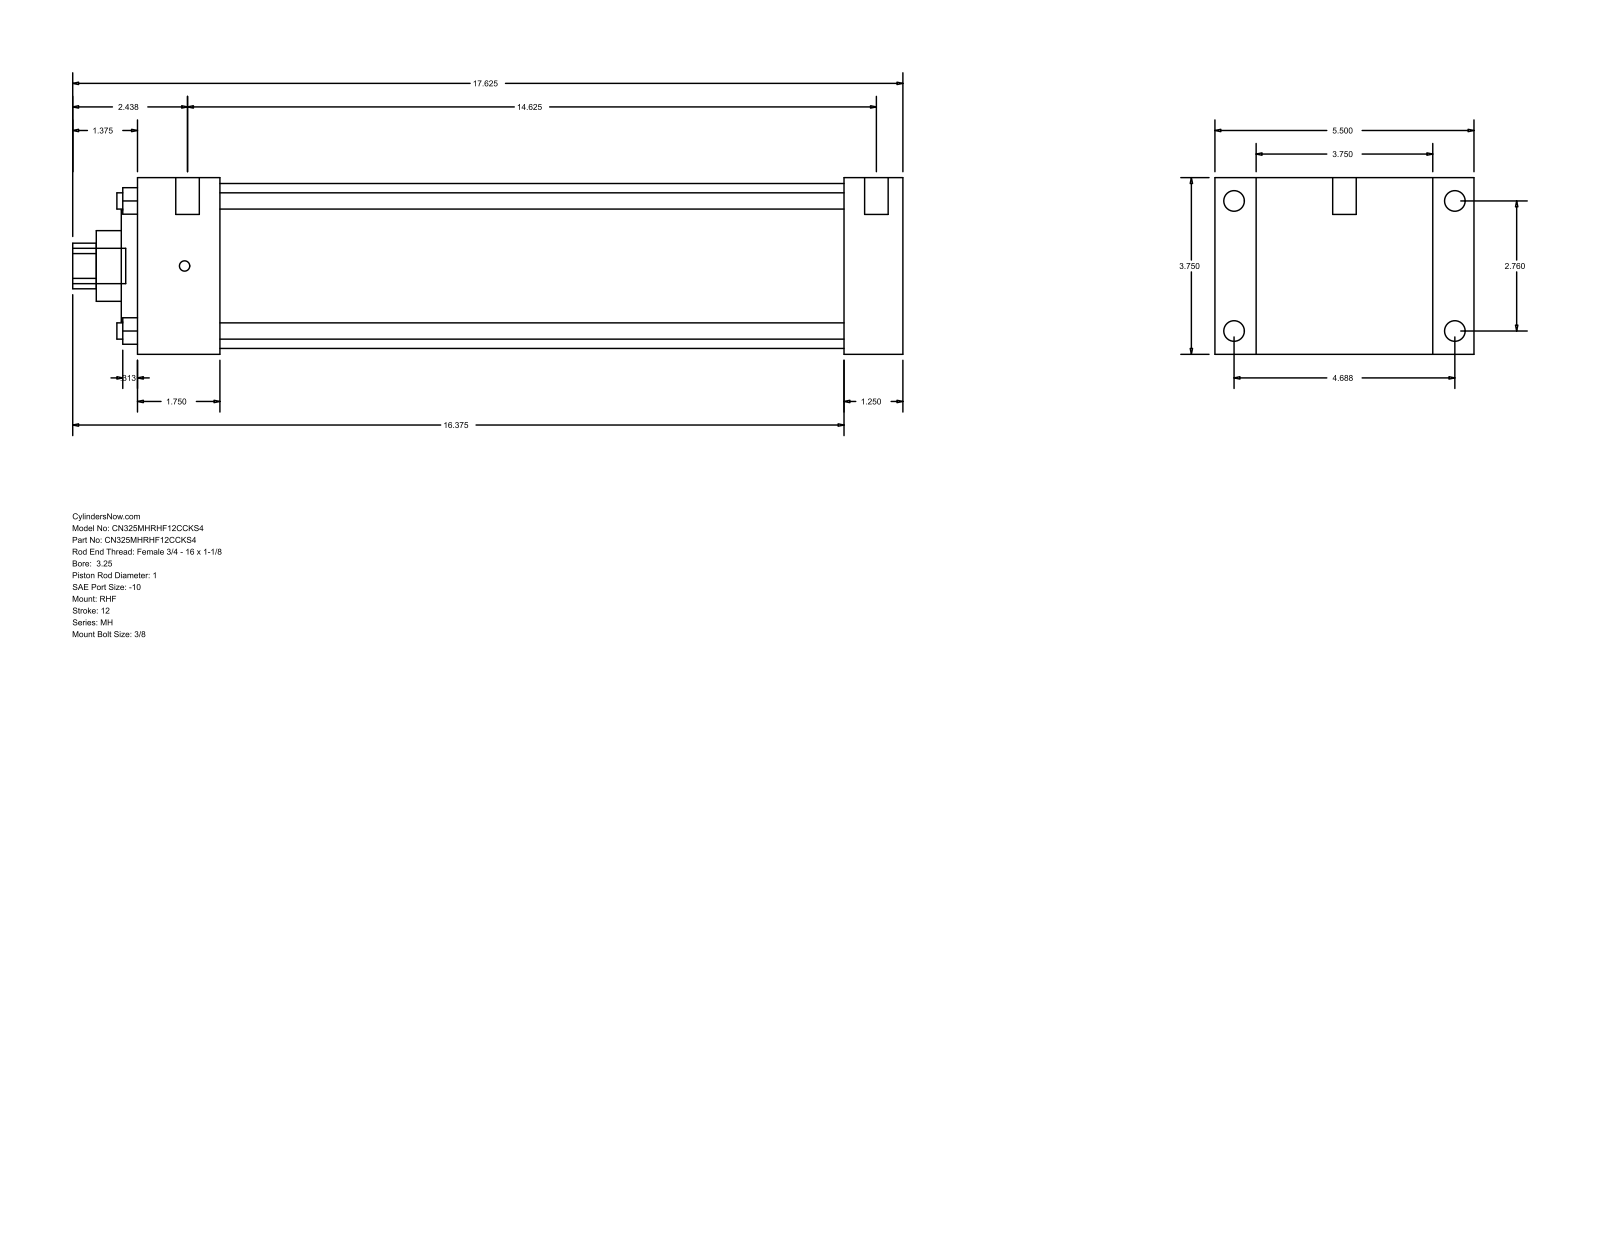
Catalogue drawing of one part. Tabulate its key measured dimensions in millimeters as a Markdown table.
| quantity | value |
| --- | --- |
| part name | MH_RHF__0325_1 |
| STEP written by | GSSL Pune (CONFIG_CONTROL_DESIGN) |
| units | millimeters |
| bodies | 0 solids, 90 faces (61 planar, 29 cylindrical, 0 other) |
| overall size | 447.68 × 139.7 × 95.25 |
| round holes (diameter × count) | 8.76 × 4, 25.4 × 1, 38.1 × 1, 60.33 × 1, 88.9 × 1 |
| round bosses / shafts (diameter × count) | 11.13 × 4, 5.56 × 4, 12.7 × 2, 19.05 × 1 |
| partial cylindrical surfaces (radius × count) | 12.29 × 1 |
| main face-to-face distances | 95.24, 31.75, 22.23, 117.47, 381.01, 412.76, 139.7, 44.46, 336.55, 368.3 |
| hole center spacings | 49.57, 70.1, 99.14 |
